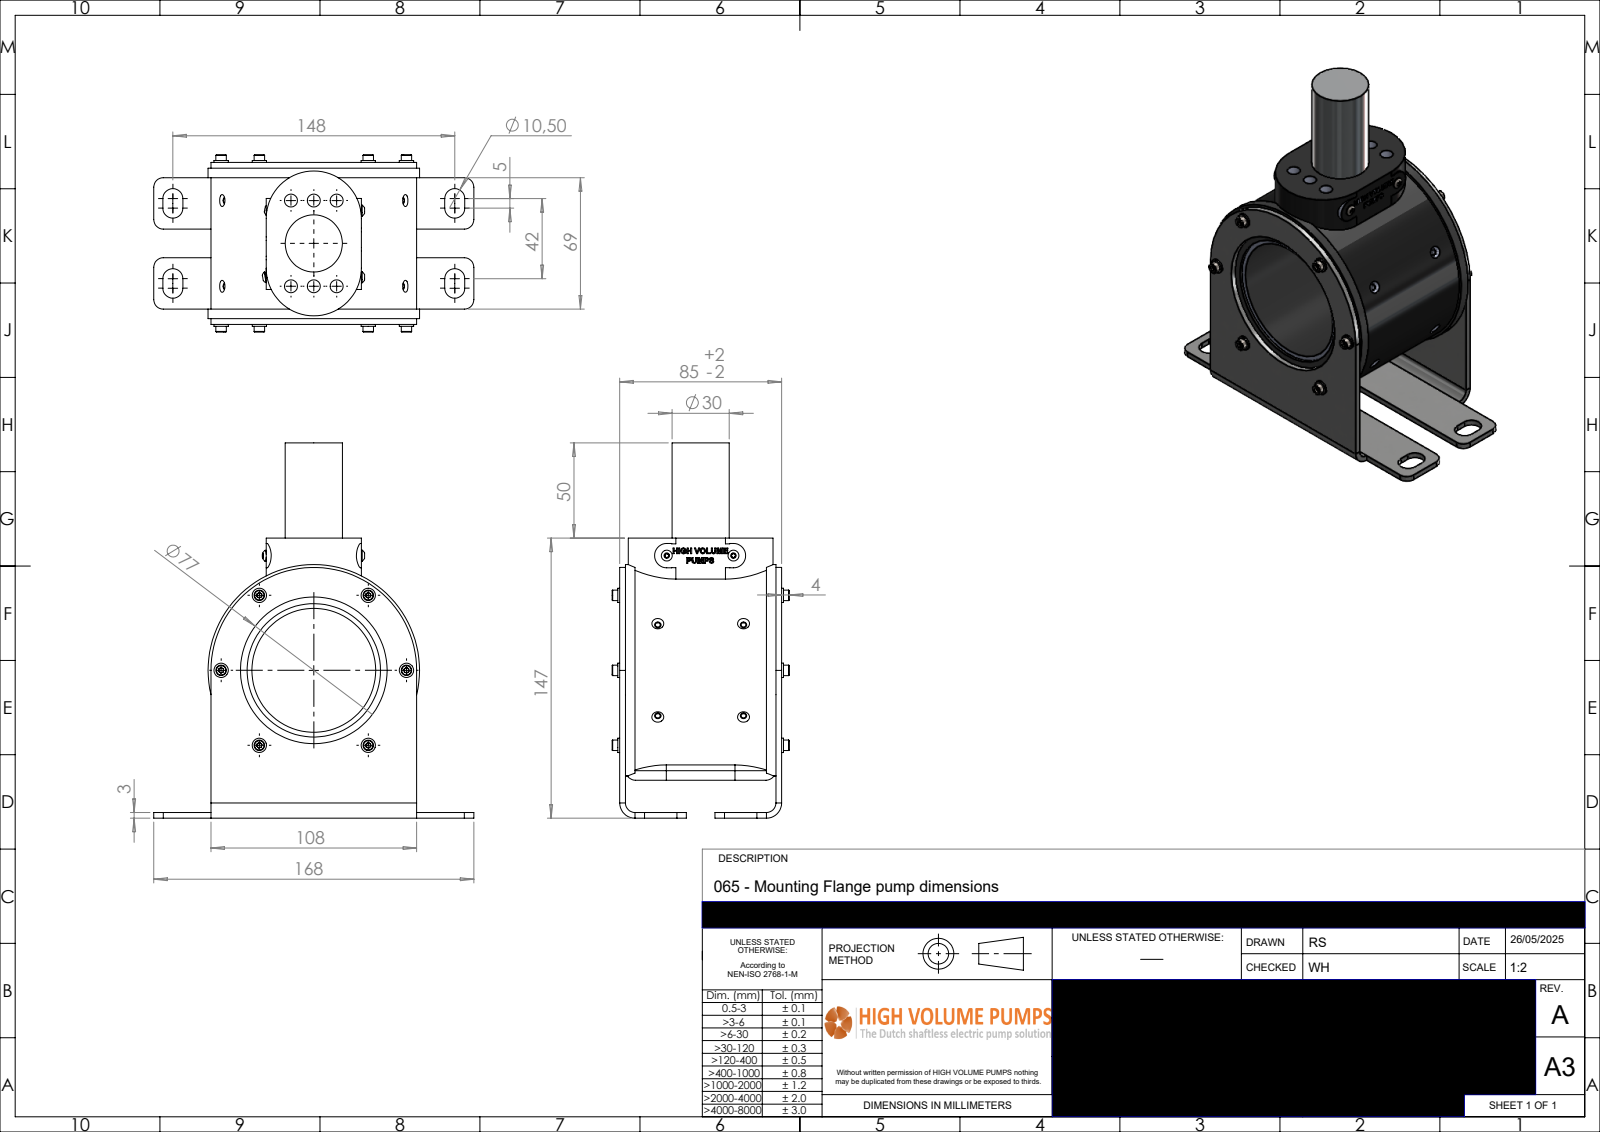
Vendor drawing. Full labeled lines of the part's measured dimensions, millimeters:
Part name (STEP PRODUCT): P-065-030-rev-A-MF
STEP written by: SolidWorks 2024 (AUTOMOTIVE_DESIGN)
Units: millimetres
Bodies: 1 solid, 879 faces (587 planar, 109 cylindrical, 183 other)
Overall size (bounding box): 196.96 × 168 × 93
Volume: 644 662 mm³ · Surface area: 107 278 mm²
Round holes (diameter × count): ⌀2.5 ×6, ⌀3.6 ×6, ⌀6.8 ×6, ⌀65 ×1, ⌀70 ×1, ⌀77 ×1
Round bosses / shafts (diameter × count): ⌀7.5 ×6, ⌀5.5 ×6, ⌀3 ×6, ⌀5.7 ×3, ⌀111 ×1, ⌀108 ×1, ⌀30 ×1
Partial cylindrical surfaces — rounded edges, fillets, slot ends (radius × count): R5 ×12, R5.25 ×8, R2 ×3, R6.4 ×2, R8 ×2, R21.25 ×2, R25 ×2, R1.5 ×1
Main face-to-face distances: 3, 82, 85, 79, 50, 146.97, 143.97, 19.96, 16.96, 127.01
Hole centre spacings: 45, 48.65, 12, 46.57, 86.69, 24, 44.17, 51
